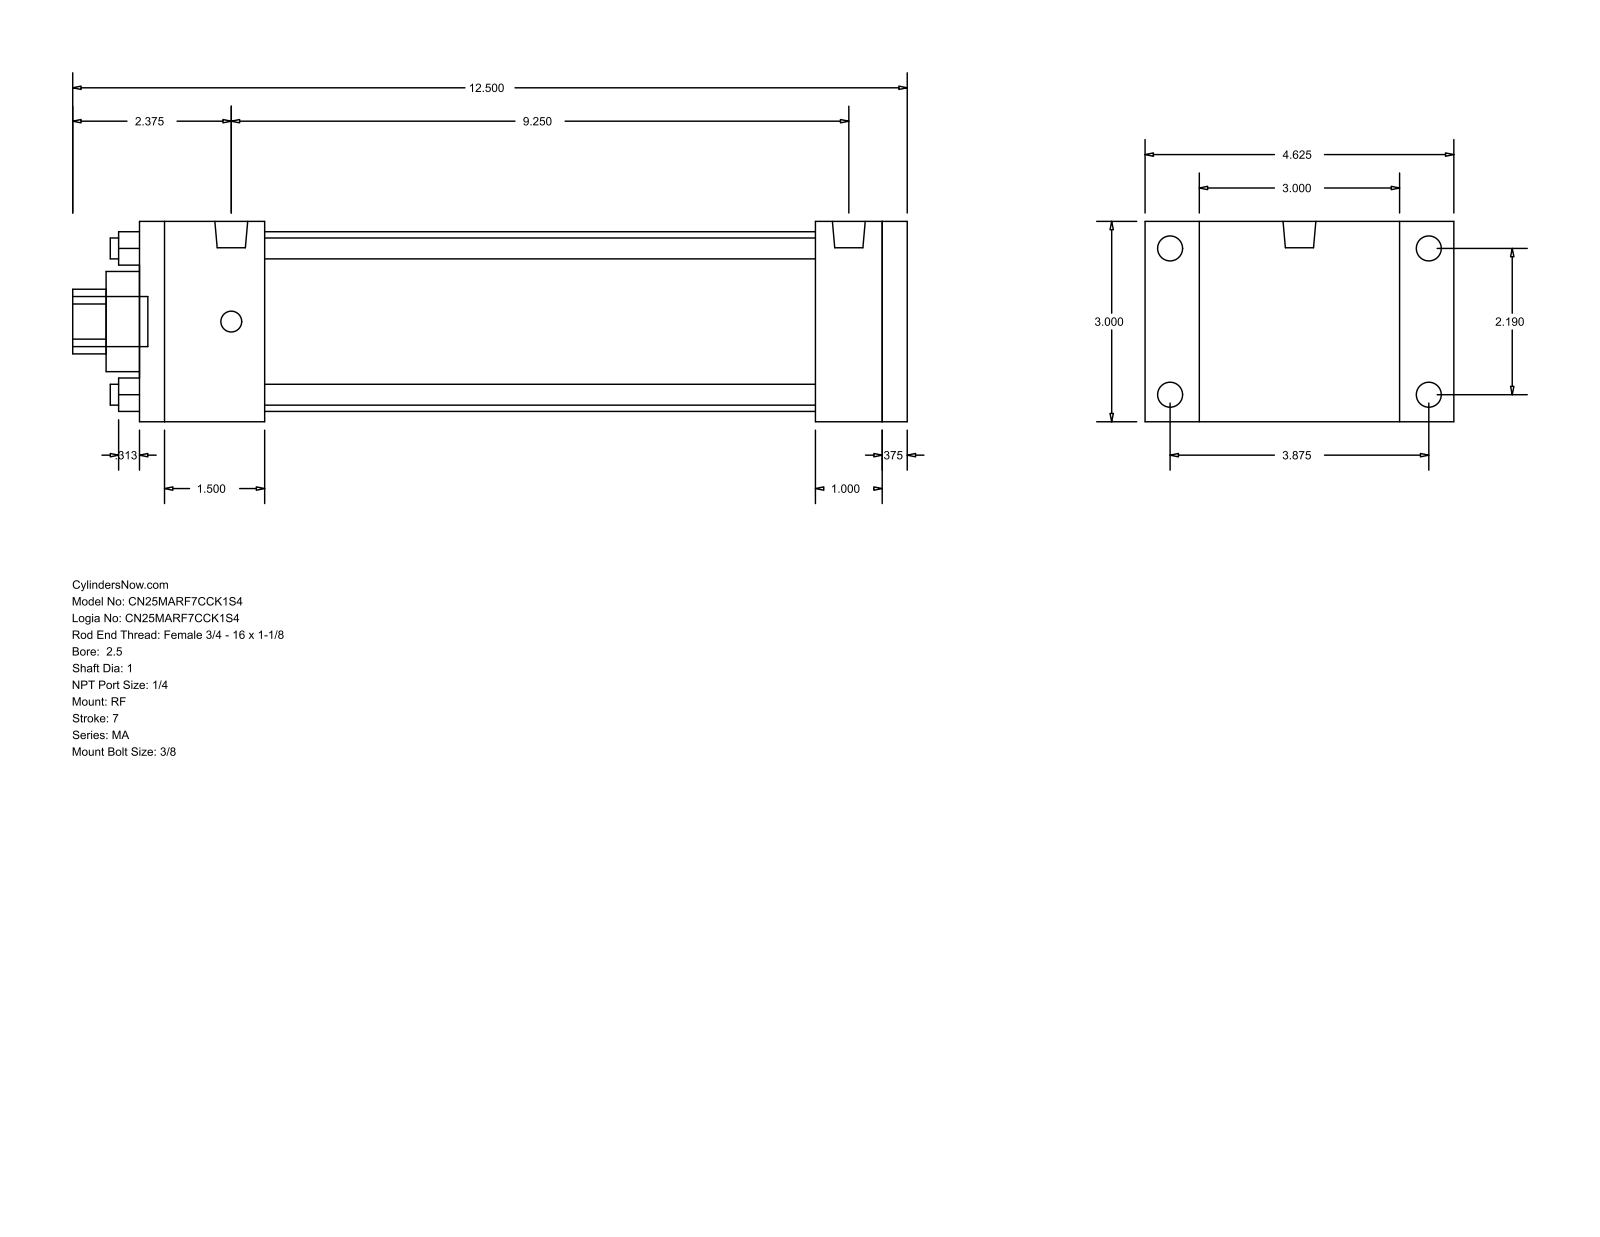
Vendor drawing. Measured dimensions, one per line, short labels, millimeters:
name: MA_RF__0250_1
written by: GSSL Pune (CONFIG_CONTROL_DESIGN)
unit: mm
bodies: 0 solids, 92 faces (64 planar, 28 cylindrical, 0 other)
size: 317.5 × 117.47 × 76.2
holes: 4× ⌀7.94, 1× ⌀25.4, 1× ⌀38.1, 1× ⌀68.33
bosses: 4× ⌀9.53, 4× ⌀7.94, 2× ⌀12.49, 1× ⌀19.05
rounds: 1× R12.29
face distances: 76.2, 292.1, 282.58, 9.52, 47.63, 257.17, 209.54, 234.95, 244.47, 25.41
hole spacings: 39.33, 55.62, 78.66
